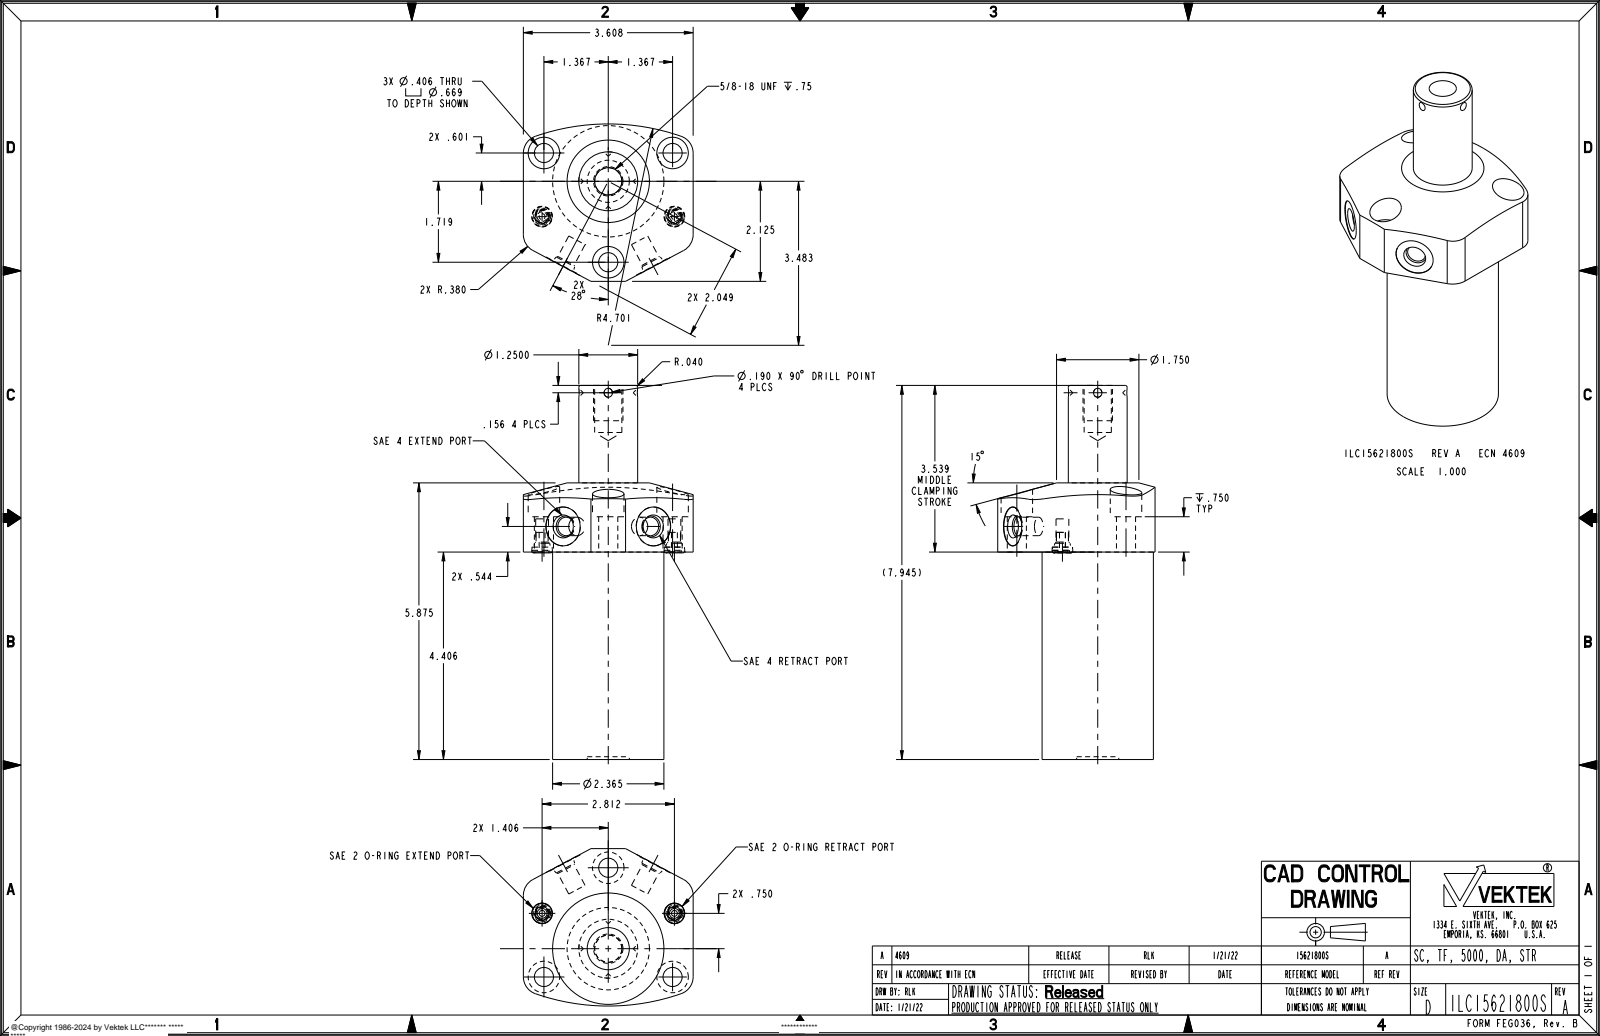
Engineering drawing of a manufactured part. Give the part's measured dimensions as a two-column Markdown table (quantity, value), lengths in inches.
| quantity | value |
| --- | --- |
| part name | ILC15621800S |
| STEP written by | CREO PARAMETRIC BY PTC INC, 2021164 (AUTOMOTIVE_DESIGN) |
| units | inches |
| bodies | 1 solid, 129 faces (32 planar, 59 cylindrical, 38 other) |
| overall size | 7.945 × 3.808 × 3.543 |
| volume | 34.63 in³ |
| surface area | 89.87 in² |
| round holes (diameter × count) | 0.406 × 3, 0.669 × 3, 0.125 × 2, 0.272 × 2, 0.392 × 2, 0.438 × 2, 0.825 × 2, 0.578 × 1, 0.895 × 1 |
| round bosses / shafts (diameter × count) | 0.43 × 2, 0.256 × 2, 0.21 × 2, 2.365 × 1, 1.25 × 1, 0.625 × 1 |
| partial cylindrical surfaces (radius × count) | 0.38 × 4, 4.701 × 1 |
| main face-to-face distances | 4.406, 3.608, 5.875, 1.469, 7.945, 3.539, 2.07, 0.75, 2.789, 5.156 |
| hole center spacings | 1.352, 1.493, 1.593, 1.707, 2.693, 3.085, 1.719, 2.734 |
